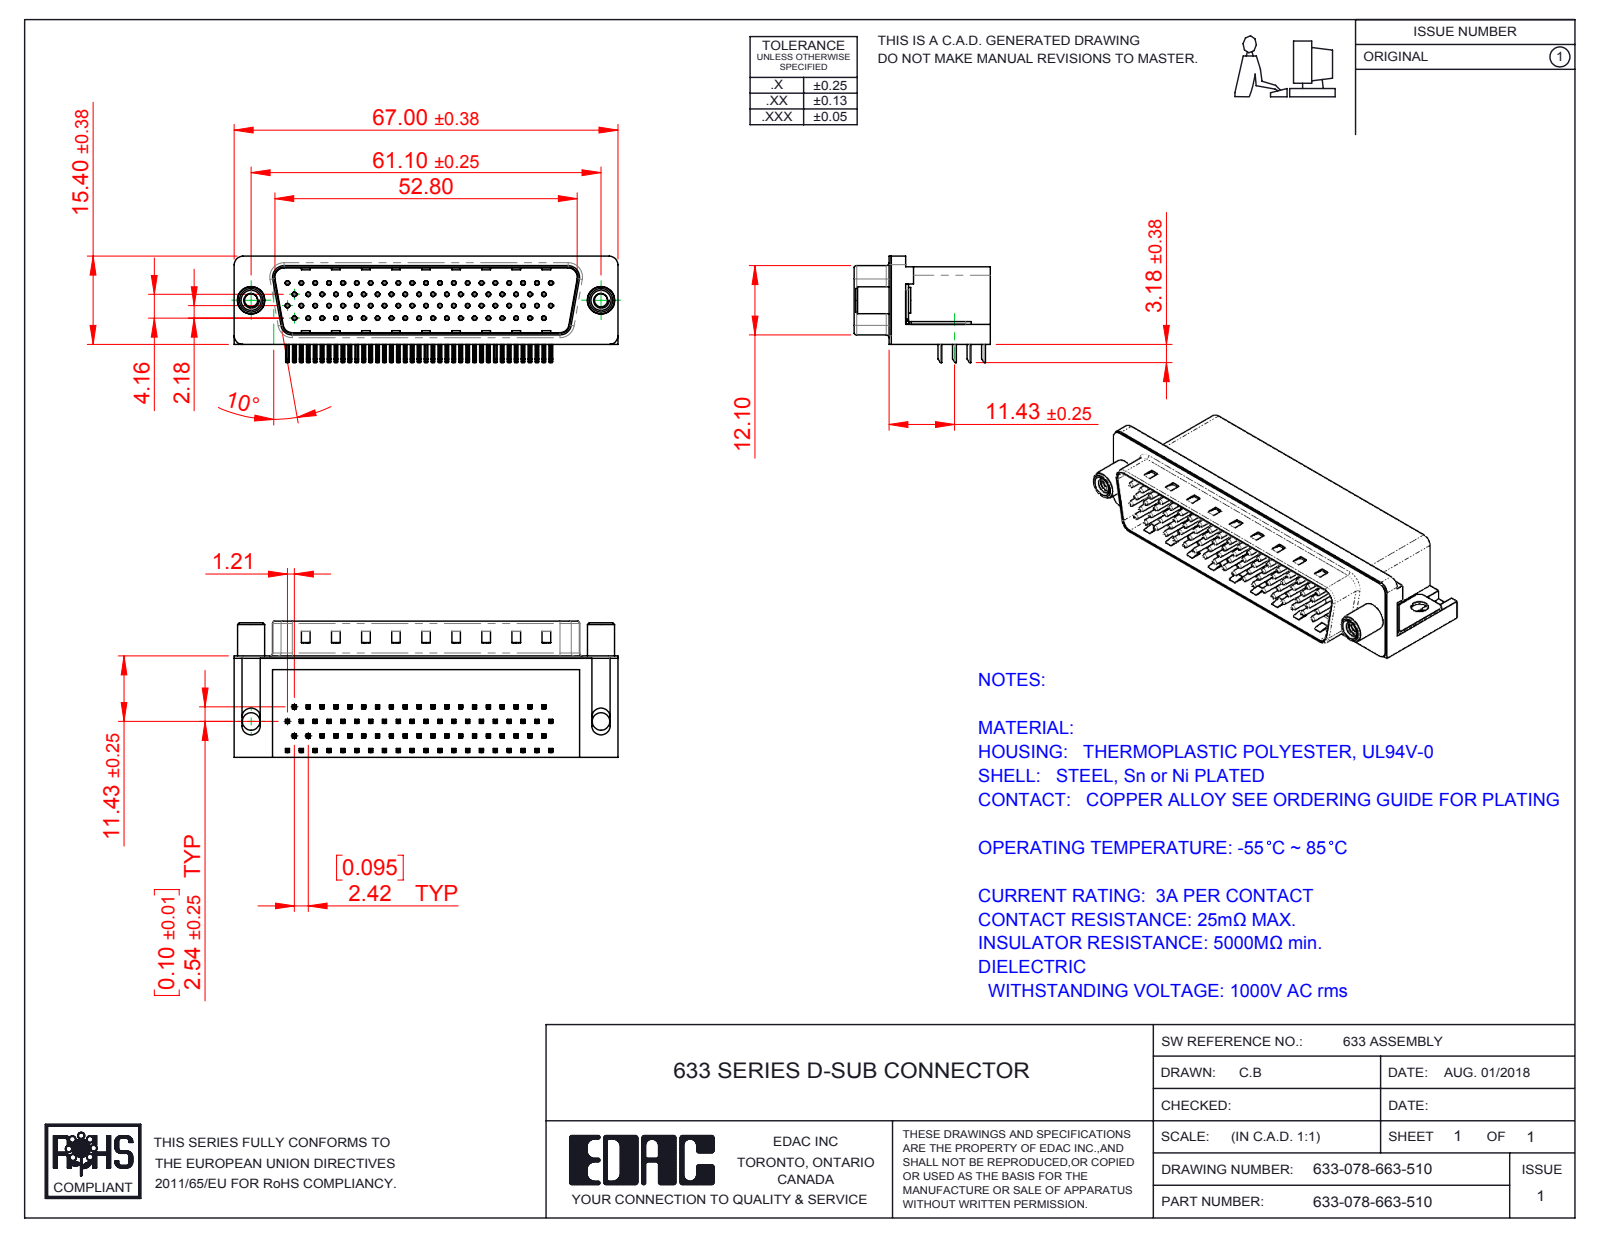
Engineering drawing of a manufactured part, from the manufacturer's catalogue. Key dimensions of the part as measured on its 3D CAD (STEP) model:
Part name (STEP PRODUCT): 633-078-663-510; 633 Housing_78 Contact; 633 Thru Hole Board Mount_78 Contact; 633 Shell_78 Contact (+5 more)
STEP written by: SolidWorks 2016 (CONFIG_CONTROL_DESIGN)
Units: millimetres
Bodies: 84 solids, 6268 faces (3971 planar, 1786 cylindrical, 511 other)
Overall size (bounding box): 67 × 23.8 × 18.58
Volume: 14 701 mm³ · Surface area: 16 535 mm²
Round holes (diameter × count): ⌀0.35 ×78, ⌀0.8 ×78, ⌀2.3 ×2, ⌀3.05 ×2, ⌀3.1 ×2, ⌀4 ×2, ⌀4.8 ×2, ⌀5 ×2
Round bosses / shafts (diameter × count): ⌀0.75 ×78, ⌀4.9 ×2, ⌀4.7 ×2, ⌀4.5 ×2, ⌀3.85 ×2
Partial cylindrical surfaces — rounded edges, fillets, slot ends (radius × count): R0.25 ×312, R0.12 ×156, R1 ×16, R0.5 ×9, R1.6 ×8, R1.5 ×6, R0.45 ×4, R0.9 ×4
Main face-to-face distances: 0.4, 13.2, 17.3, 11.7, 13.35, 2.05, 13.75, 1.65, 1.85, 11.9
Hole centre spacings: 2.42, 4.84, 7.26, 9.68, 6.26, 7.13, 12.1, 8.62
